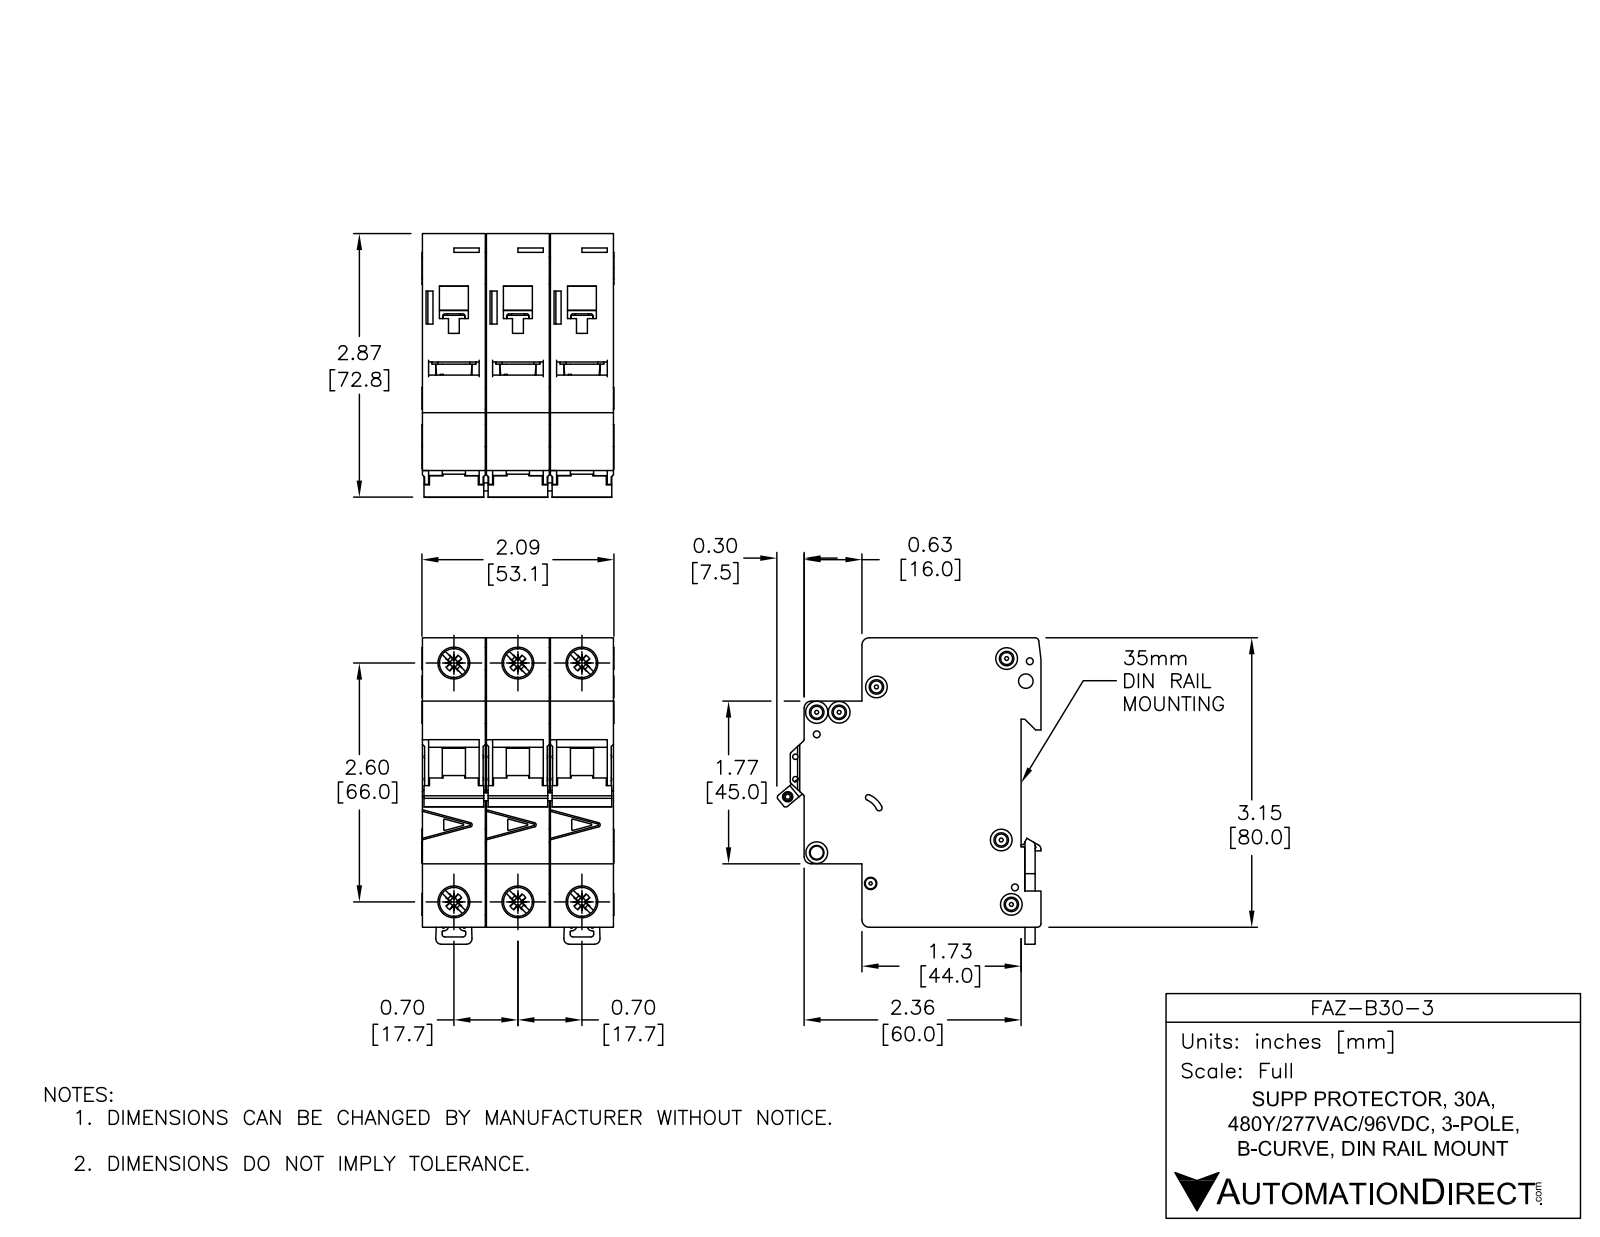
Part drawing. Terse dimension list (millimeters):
name: FAZ-B30-3
written by: SolidWorks 2014 (AUTOMOTIVE_DESIGN)
unit: mm
bodies: 11 solids, 1650 faces (697 planar, 590 cylindrical, 363 other)
size: 84.78 × 73.04 × 53.1
volume: 224 680 mm³; area: 58 052 mm²
holes: 6× ⌀3.6, 4× ⌀8.2, 3× ⌀1.9, 2× ⌀1.09, 2× ⌀1.5, 2× ⌀4, 2× ⌀7.15, 1× ⌀2.15, 1× ⌀2.2, 1× ⌀2.55, 1× ⌀3.3, 1× ⌀3.4
bosses: 4× ⌀6, 3× ⌀2.5, 2× ⌀8.2
rounds: 68× R0.25, 25× R0.5, 12× R1, 12× R2, 11× R0.2, 3× R1.8, 2× R0.8, 2× R3
face distances: 17.7, 17.5, 35.4, 35.2, 52.9, 17.9, 79.48, 5.5, 49.5, 44
hole spacings: 17.7, 68.33, 66, 6.2, 13.64, 35.4, 74.89, 4.81
